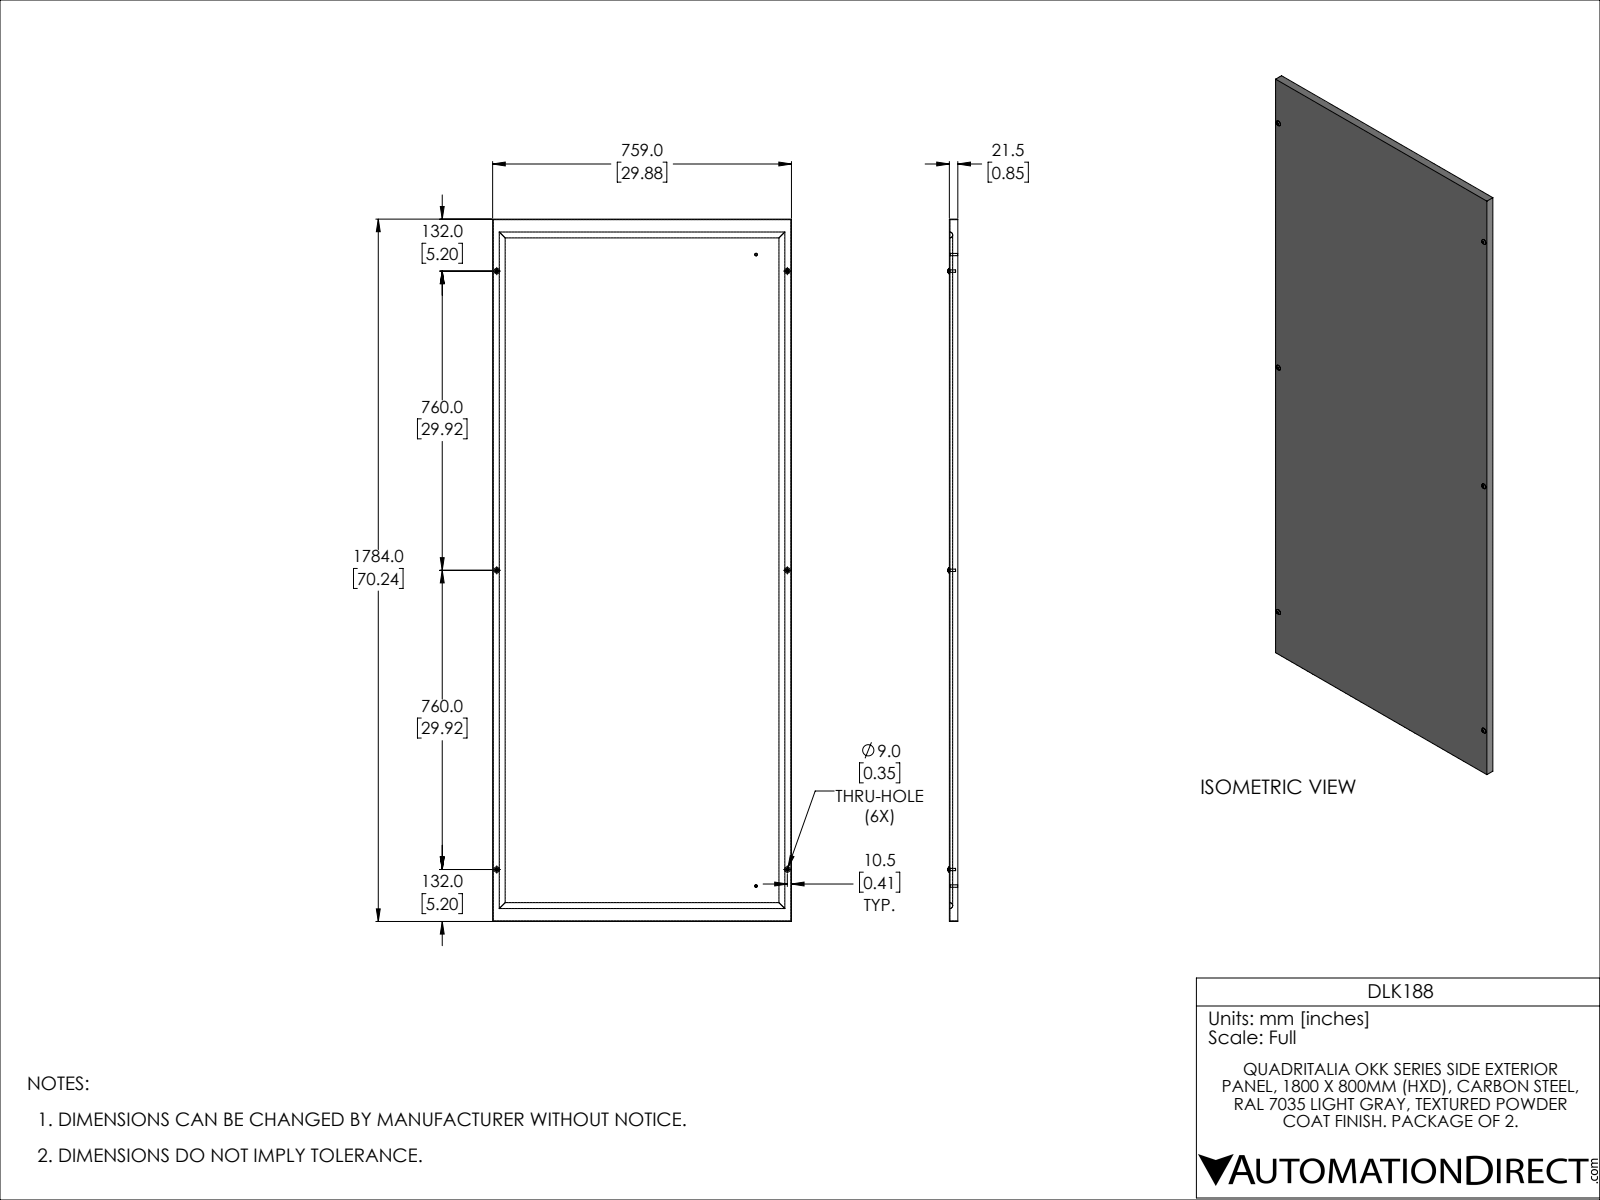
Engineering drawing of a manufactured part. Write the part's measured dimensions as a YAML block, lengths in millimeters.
part_name: "DLK188"
step_written_by: "SolidWorks 2021 (CONFIG_CONTROL_DESIGN)"
units: millimeters
bodies: {solids: 13, faces: 243, planar: 125, cylindrical: 98, other: 20}
overall_size: [1784, 759, 25.2]
volume: 2579000
surface_area: 3106000
round_holes:
  - {diameter: 9, count: 6}
round_bosses_or_shafts:
  - {diameter: 6, count: 8}
  - {diameter: 14, count: 6}
  - {diameter: 7, count: 2}
partial_cylinders:
  - {radius: 0.5, count: 72}
  - {radius: 7.5, count: 4}
face_to_face_distances: [1.5, 757.5, 759, 756, 1782.5, 1784, 1781, 21.5, 20, 702.1]
hole_center_spacings: [760, 1059.4, 738, 1520, 1689.7]
